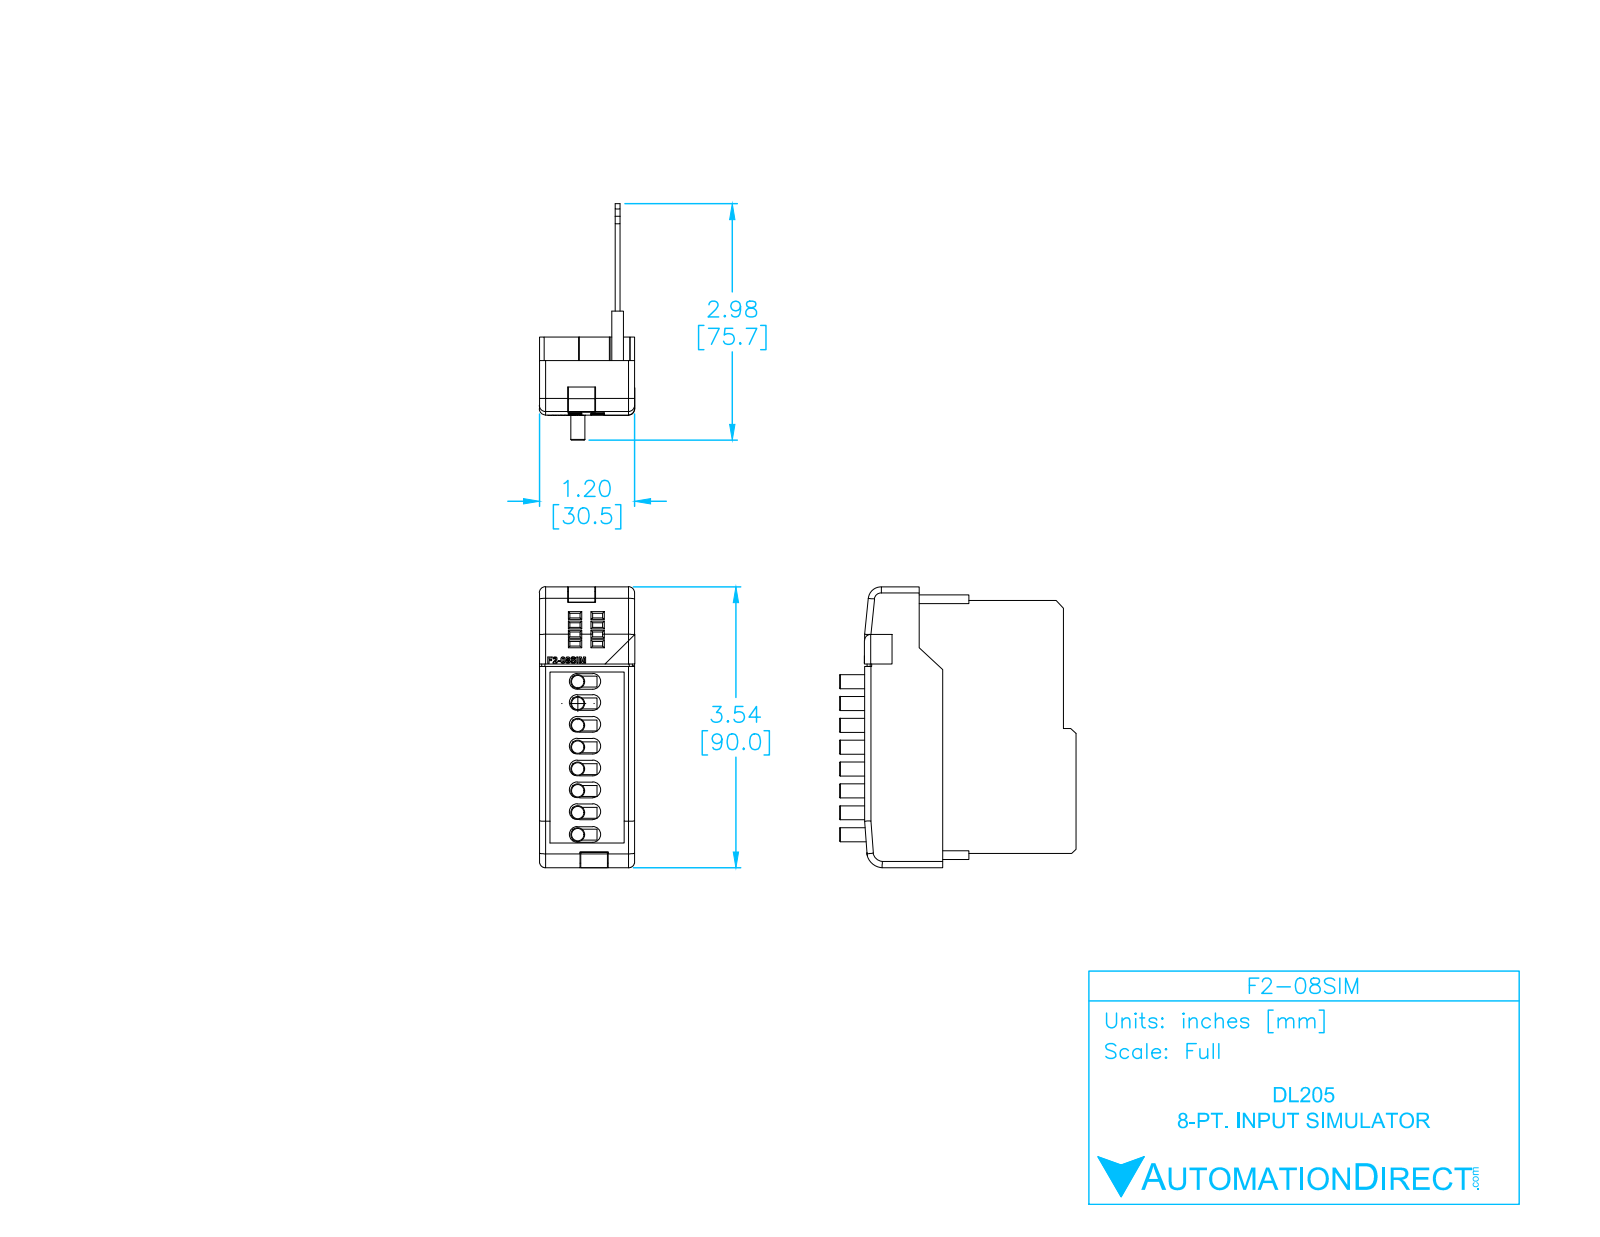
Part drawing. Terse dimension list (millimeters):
name: F2-SIM_ModuleCase_light_NEW
written by: SolidWorks 2009 (AUTOMOTIVE_DESIGN)
unit: mm
bodies: 10 solids, 533 faces (333 planar, 121 cylindrical, 79 other)
size: 90 × 75.72 × 30.55
volume: 25 166 mm³; area: 32 969 mm²
bosses: 8× ⌀4.5
rounds: 29× R0.5, 16× R2.5, 11× R2, 4× R0.25, 2× R1, 1× R2.62, 1× R3.79, 1× R4.12
face distances: 1.5, 4.72, 0.5, 3.22, 6.22, 24.28, 29, 7.75, 8.25, 7
